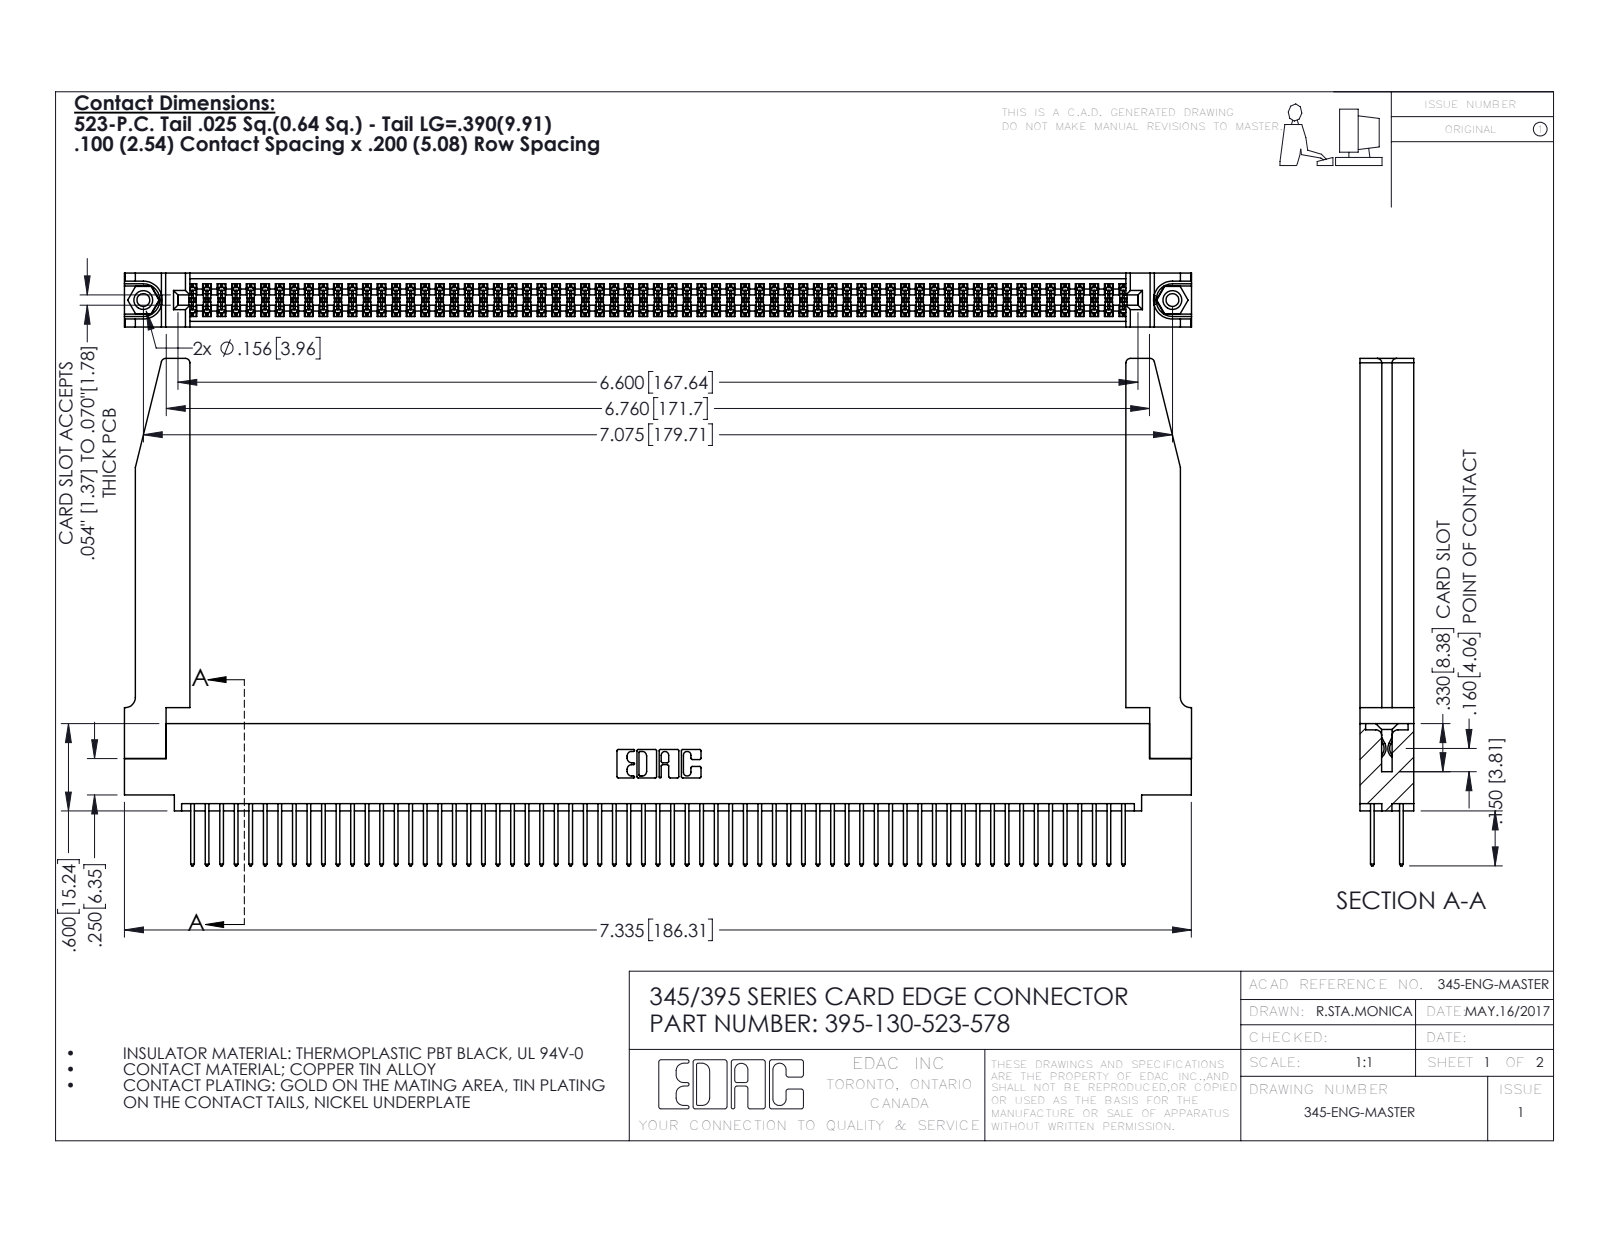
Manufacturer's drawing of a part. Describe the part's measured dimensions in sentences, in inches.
The part is named "345-292-001_345-293-123; 395-130-523-578; 345-250-001_345-250-001-102; 345 Part_0.110 Offset - 0.156 Dia-TH (+1 more)". Its 3-D file was written by "SolidWorks 2016 (CONFIG_CONTROL_DESIGN)". It is 135 solids with 6864 faces: 4516 planar, 2296 cylindrical and 52 other. Overall it measures 7.336 by 3.487 by 0.37 inches. Its volume is 1.604 cubic inches and its surface area 55.69 square inches. Round holes: 2 of diameter 0.089, 2 of diameter 0.125, 2 of diameter 0.156, 1 of diameter 0.064. Round bosses or shafts: 2 of diameter 0.155. Partial cylindrical surfaces (rounded edges, fillets, slot ends): 195 of radius 0.006, 130 of radius 0.01, 22 of radius 0.01, 8 of radius 0.03, 6 of radius 0.007, 6 of radius 0.031, 3 of radius 0.026, 2 of radius 0.014. The main face-to-face distances are 0.072, 0.298, 0.37, 0.2, 0.098, 0.272, 0.025, 0.225, 0.175, 0.148. The hole center spacings are 0.27, 6.839, 7.075.
